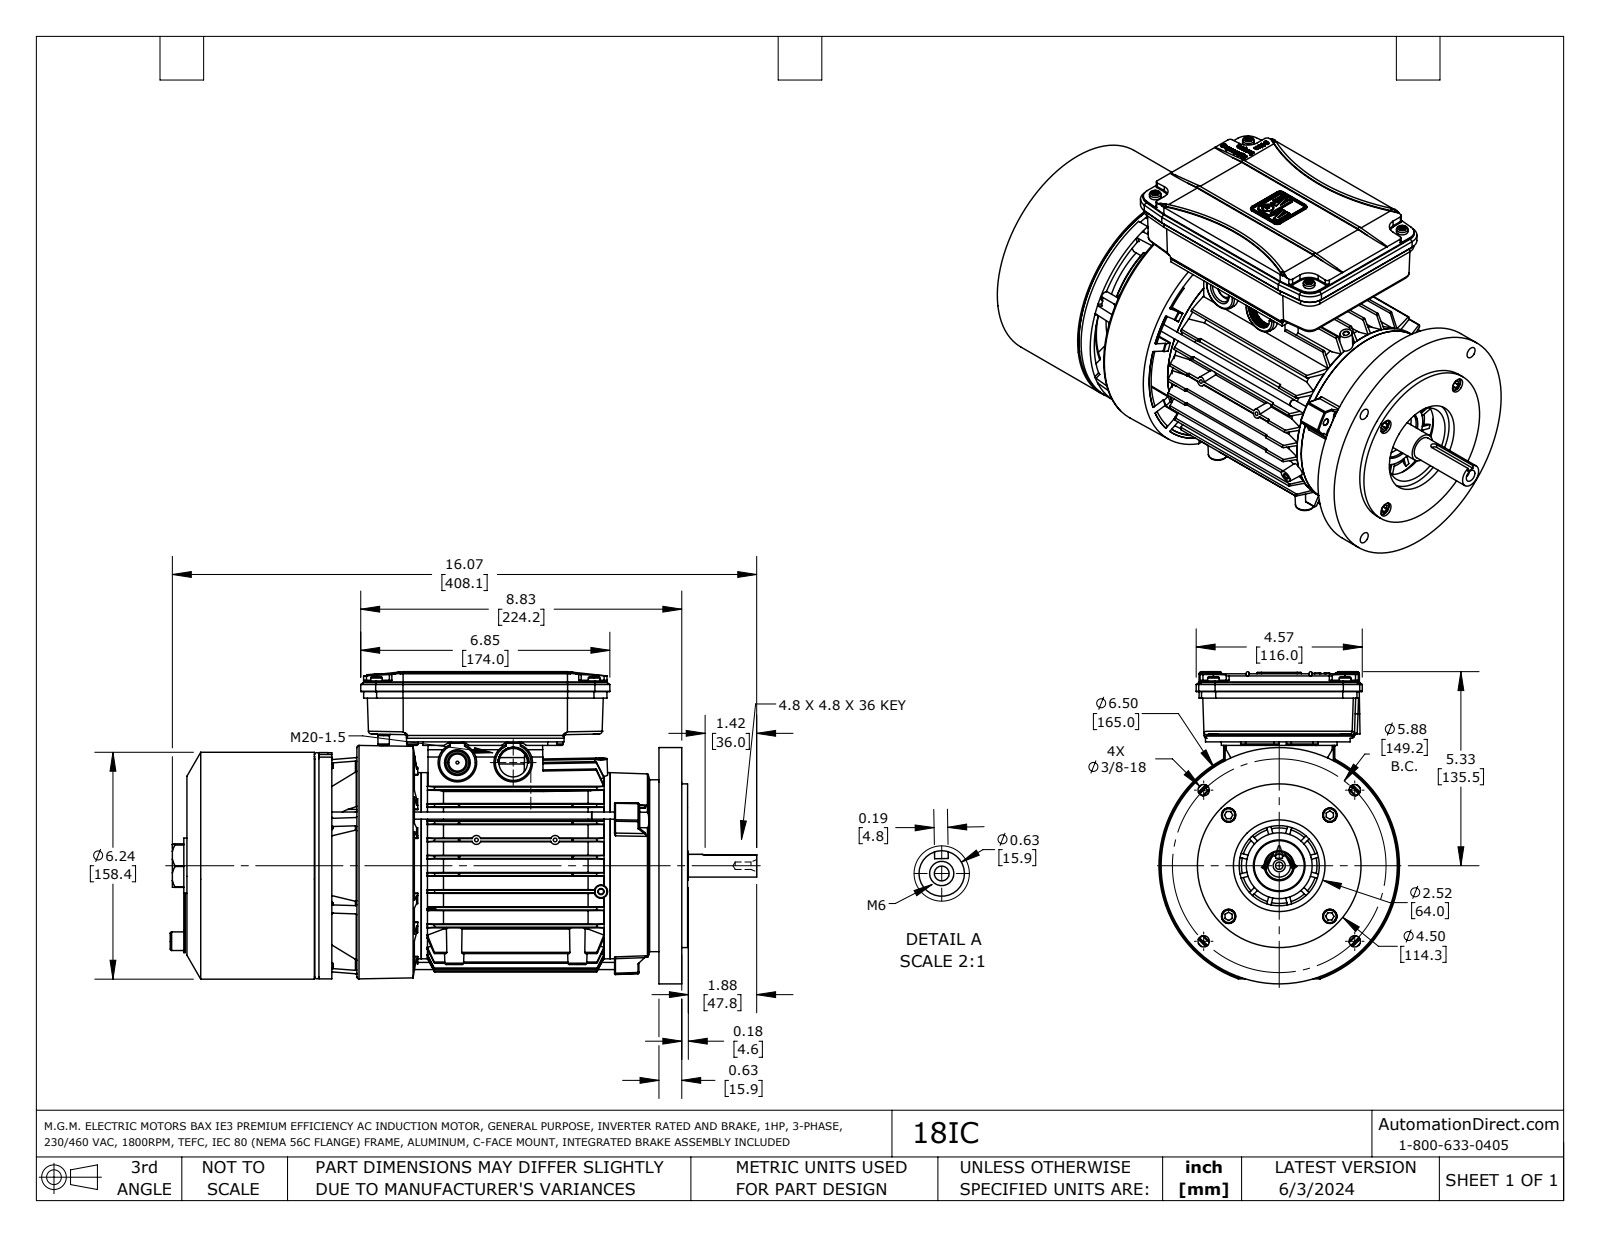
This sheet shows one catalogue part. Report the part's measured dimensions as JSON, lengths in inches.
{"part_name": "18IC", "step_written_by": "SolidWorks 2021 (AUTOMOTIVE_DESIGN)", "units": "inches", "bodies": {"solids": 26, "faces": 3575, "planar": 1231, "cylindrical": 1060, "other": 1284}, "overall_size": [16.128, 8.583, 6.614], "volume_in3": 95.95, "surface_area_in2": 1344, "round_holes": [[0.236, 15], [0.13, 14], [0.177, 12], [0.146, 8], [0.157, 8], [0.217, 8], [0.098, 7], [0.118, 4], [0.197, 4], [0.313, 4], [0.394, 4], [0.181, 3]], "round_bosses_or_shafts": [[0.177, 8], [0.118, 8], [0.386, 4], [0.315, 4], [0.197, 3], [1.063, 2], [0.248, 2], [6.496, 1]], "partial_cylinders_radius": [[0.039, 74], [0.008, 56], [0.02, 56], [0.079, 35], [0.035, 30], [0.012, 24], [0.004, 16], [0.087, 16]], "face_to_face_distances": [0.079, 0.394, 12.981, 12.933, 0.047, 0.078, 0.628, 13.561, 13.608, 0.276], "hole_center_spacings": [0.472, 3.536, 0.819, 2.756, 3.272, 0.473, 0.743, 0.785]}
